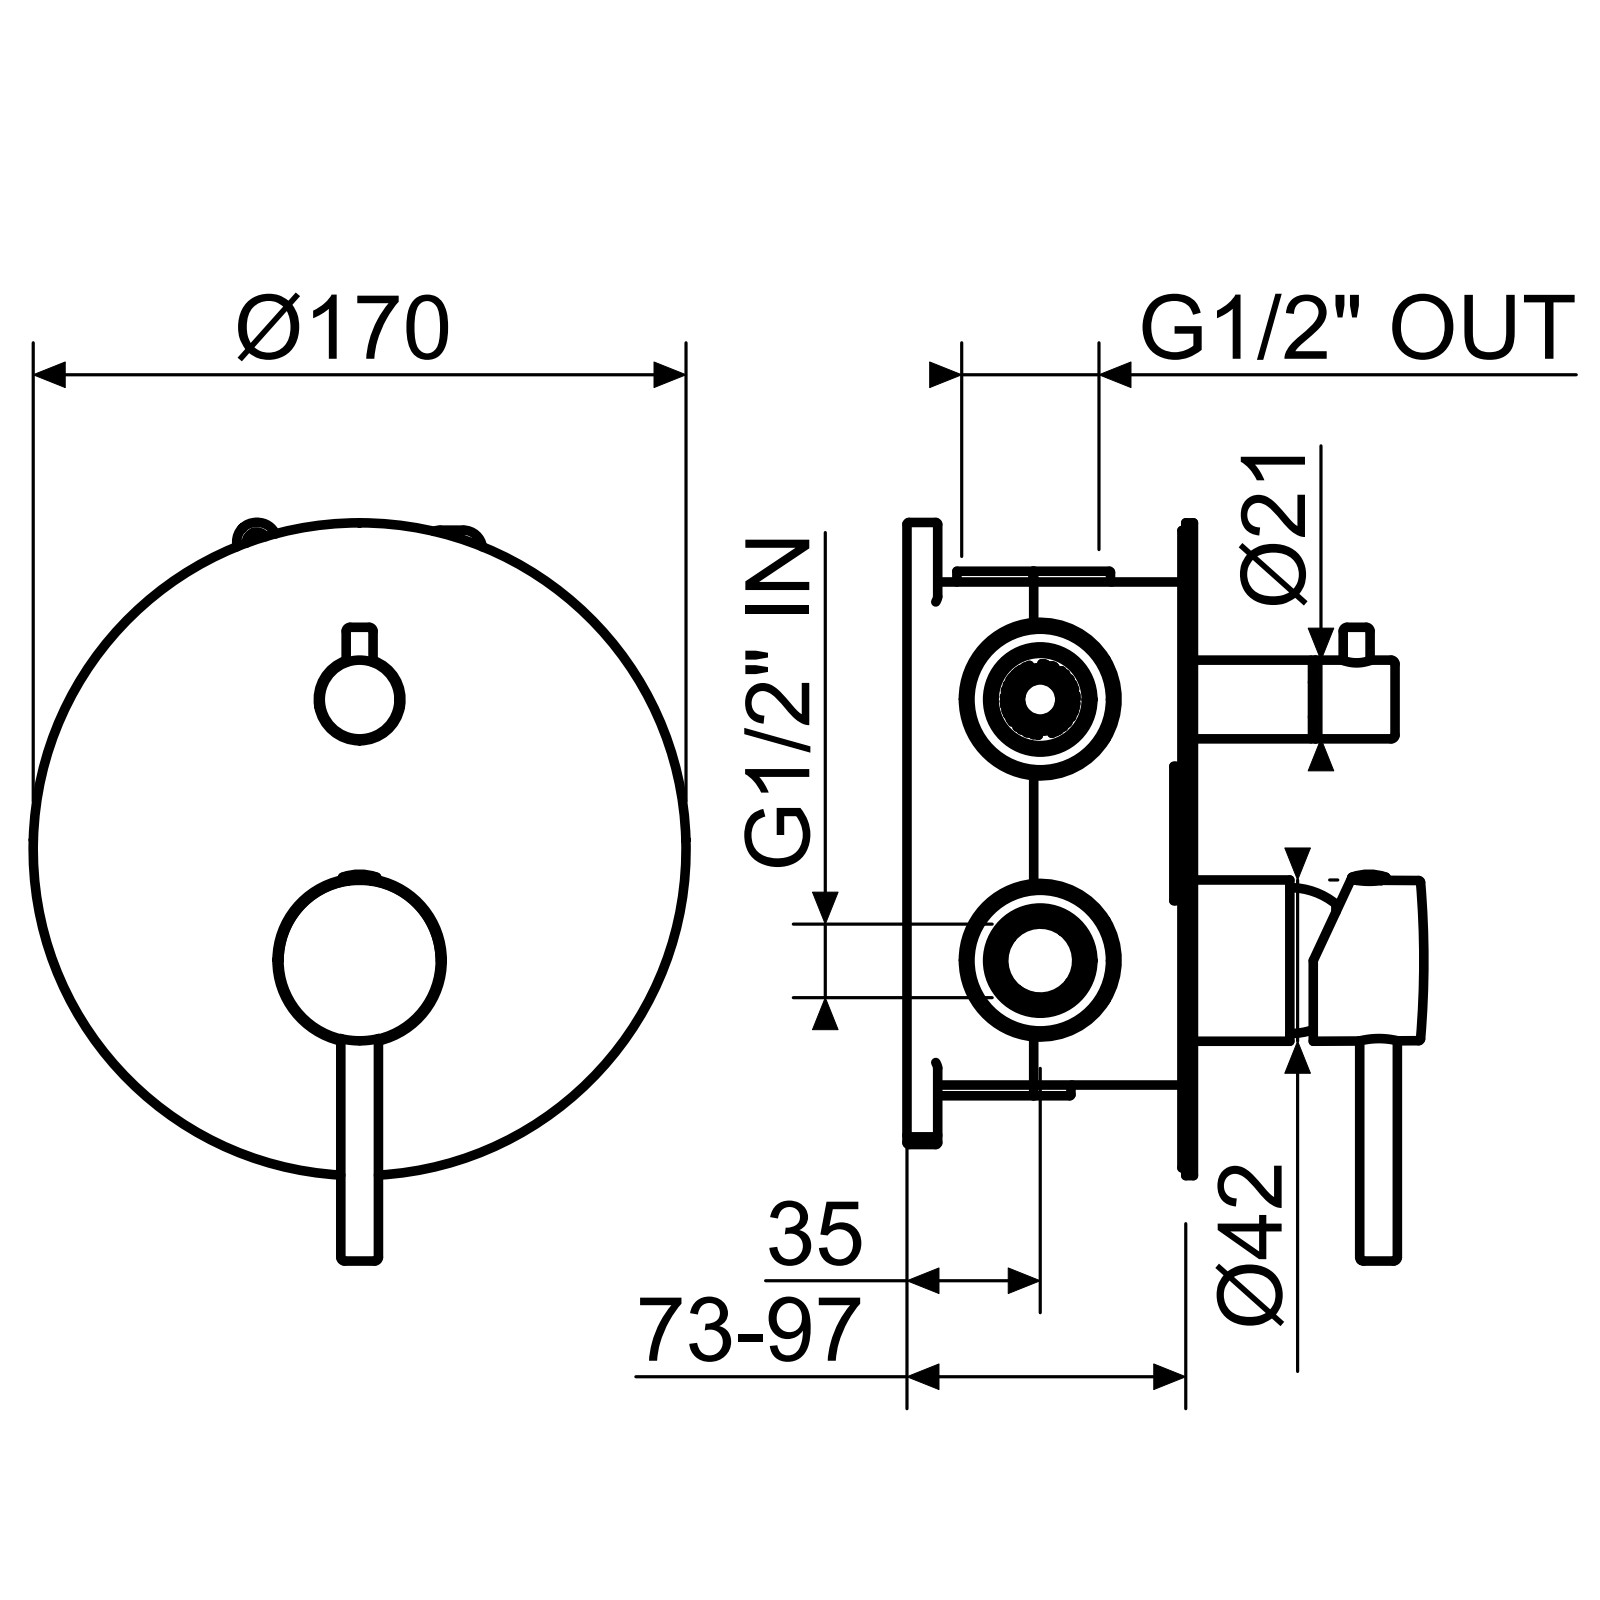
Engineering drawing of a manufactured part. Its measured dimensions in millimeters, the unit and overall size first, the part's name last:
Units: millimetres
Overall size (bounding box): 190.5 × 170 × 70.5
Round holes (diameter × count): ⌀4.2 ×3, ⌀8 ×3, ⌀5 ×2, ⌀5.1 ×1, ⌀5.2 ×1, ⌀6.5 ×1, ⌀7.5 ×1, ⌀12 ×1, ⌀14 ×1, ⌀18 ×1, ⌀21.5 ×1, ⌀22 ×1
Round bosses / shafts (diameter × count): ⌀170 ×1, ⌀49 ×1, ⌀42 ×1, ⌀41.5 ×1, ⌀36.8 ×1, ⌀27.5 ×1, ⌀20.5 ×1, ⌀7 ×1
Partial cylindrical surfaces — rounded edges, fillets, slot ends (radius × count): R0.1 ×16, R1 ×14, R0.5 ×11, R2 ×4, R1.5 ×2, R2.6 ×2, R3 ×2, R4.8 ×2
Main face-to-face distances: 2, 56, 58, 54, 4, 6, 28, 62, 60, 26
Hole centre spacings: 1, 11.5, 12.5, 68
Volume: 68 835 mm³ · Surface area: 80 666 mm²
Bodies: 12 solids, 446 faces (97 planar, 167 cylindrical, 182 other)
Part name (STEP PRODUCT): SINMAC0010; SCCMAC0011; ALOG005C004; ALOG005C002 (+8 more)
STEP written by: CREO PARAMETRIC BY PTC INC, 2020281 (CONFIG_CONTROL_DESIGN)
